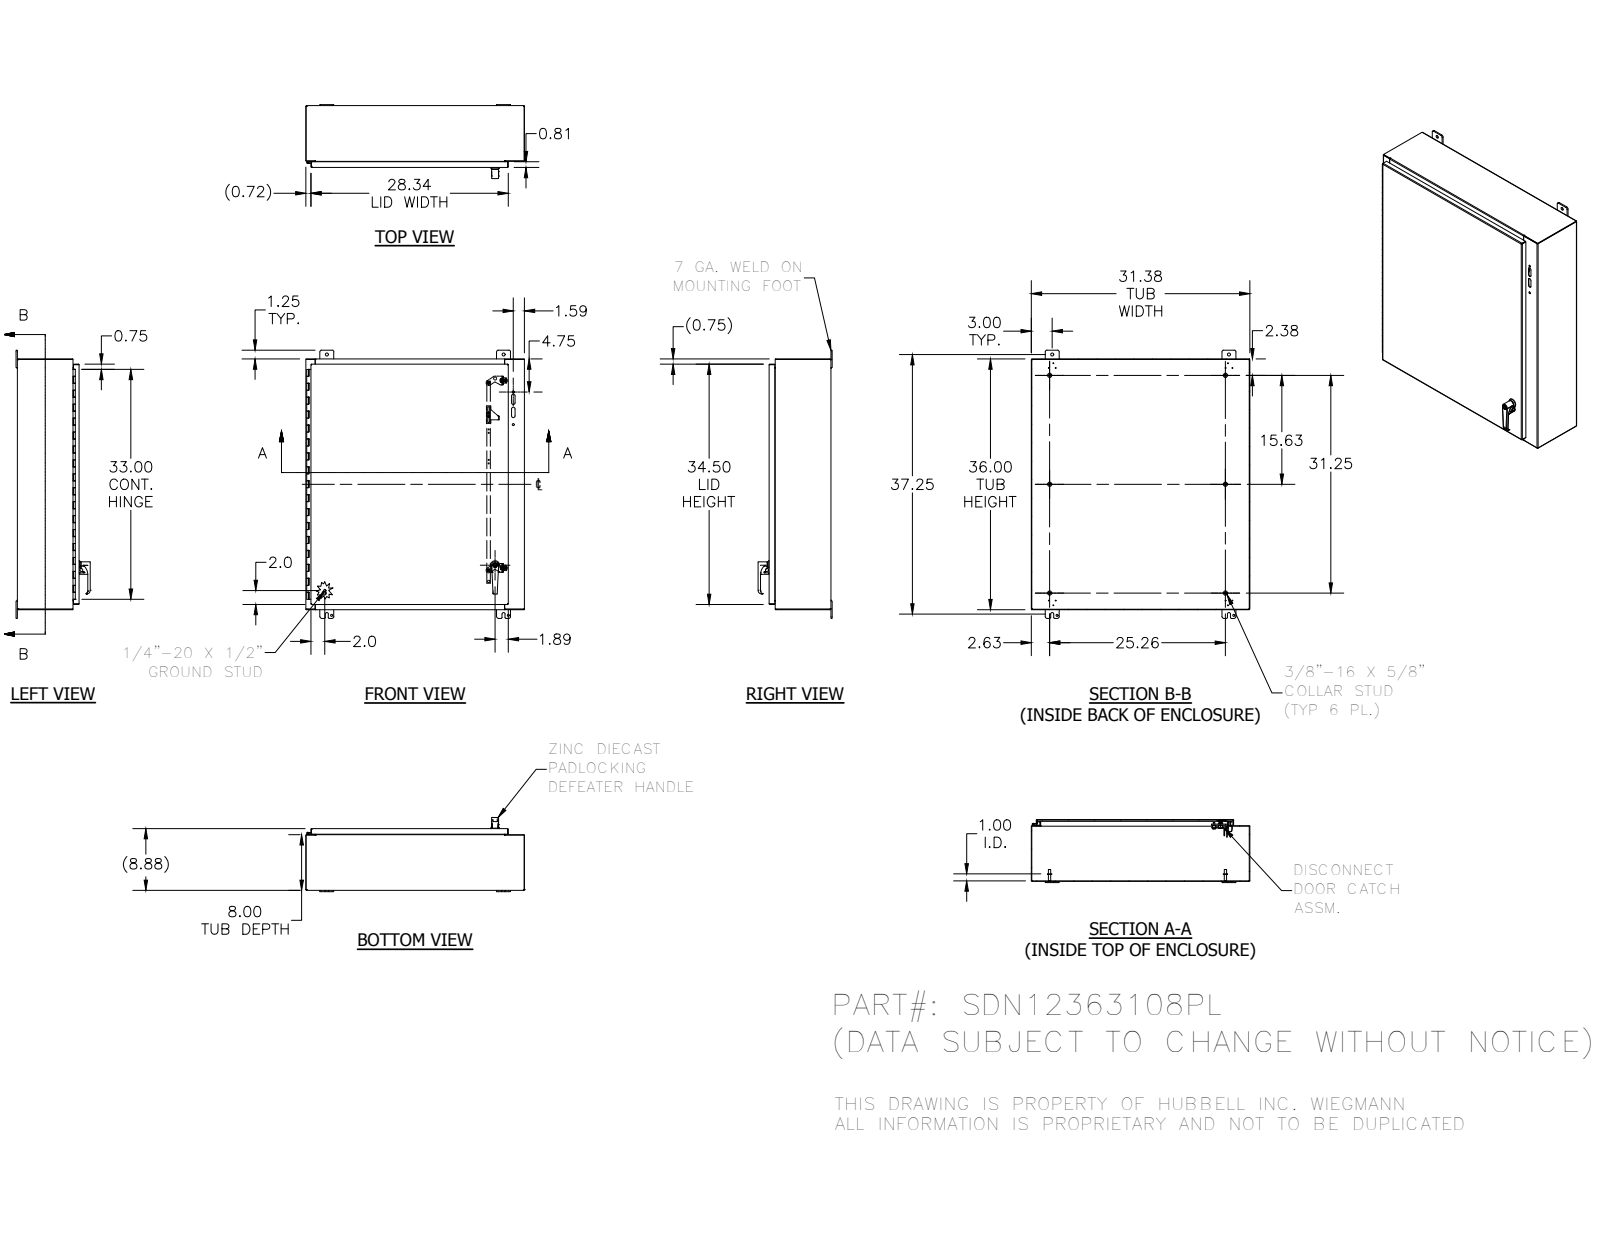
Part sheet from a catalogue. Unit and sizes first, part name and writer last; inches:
Units: inches
Overall size (bounding box): 38.5 × 31.38 × 10.649
Round holes (diameter × count): ⌀0.12 ×12, ⌀0.145 ×6, ⌀0.313 ×4, ⌀0.438 ×4, ⌀0.32 ×3, ⌀0.156 ×2, ⌀0.196 ×2, ⌀0.211 ×2, ⌀0.22 ×2, ⌀0.281 ×2, ⌀0.313 ×2, ⌀0.45 ×2
Round bosses / shafts (diameter × count): ⌀0.625 ×7, ⌀0.33 ×7, ⌀0.437 ×4, ⌀0.3 ×4, ⌀0.25 ×4, ⌀0.225 ×4, ⌀0.19 ×4, ⌀0.75 ×2
Partial cylindrical surfaces — rounded edges, fillets, slot ends (radius × count): R0.02 ×38, R0.012 ×30, R0.25 ×22, R0.031 ×20, R0.105 ×20, R0.125 ×17, R0.025 ×16, R0.07 ×8
Main face-to-face distances: 0.074, 8.801, 8.727, 8.875, 31.306, 35.926, 7.926, 0.875, 31.232, 31.38
Hole centre spacings: 26.9, 0.759, 1.593, 24.746, 25.38, 33.38, 33.394, 34.067
Volume: 280.3 in³ · Surface area: 7 498 in²
Bodies: 51 solids, 1685 faces (877 planar, 581 cylindrical, 227 other)
Part name (STEP PRODUCT): SDN12363108PL; SDN12363108PLBKP; 388116; 34840 (+8 more)
STEP written by: Autodesk Inventor 2012 (AUTOMOTIVE_DESIGN)
